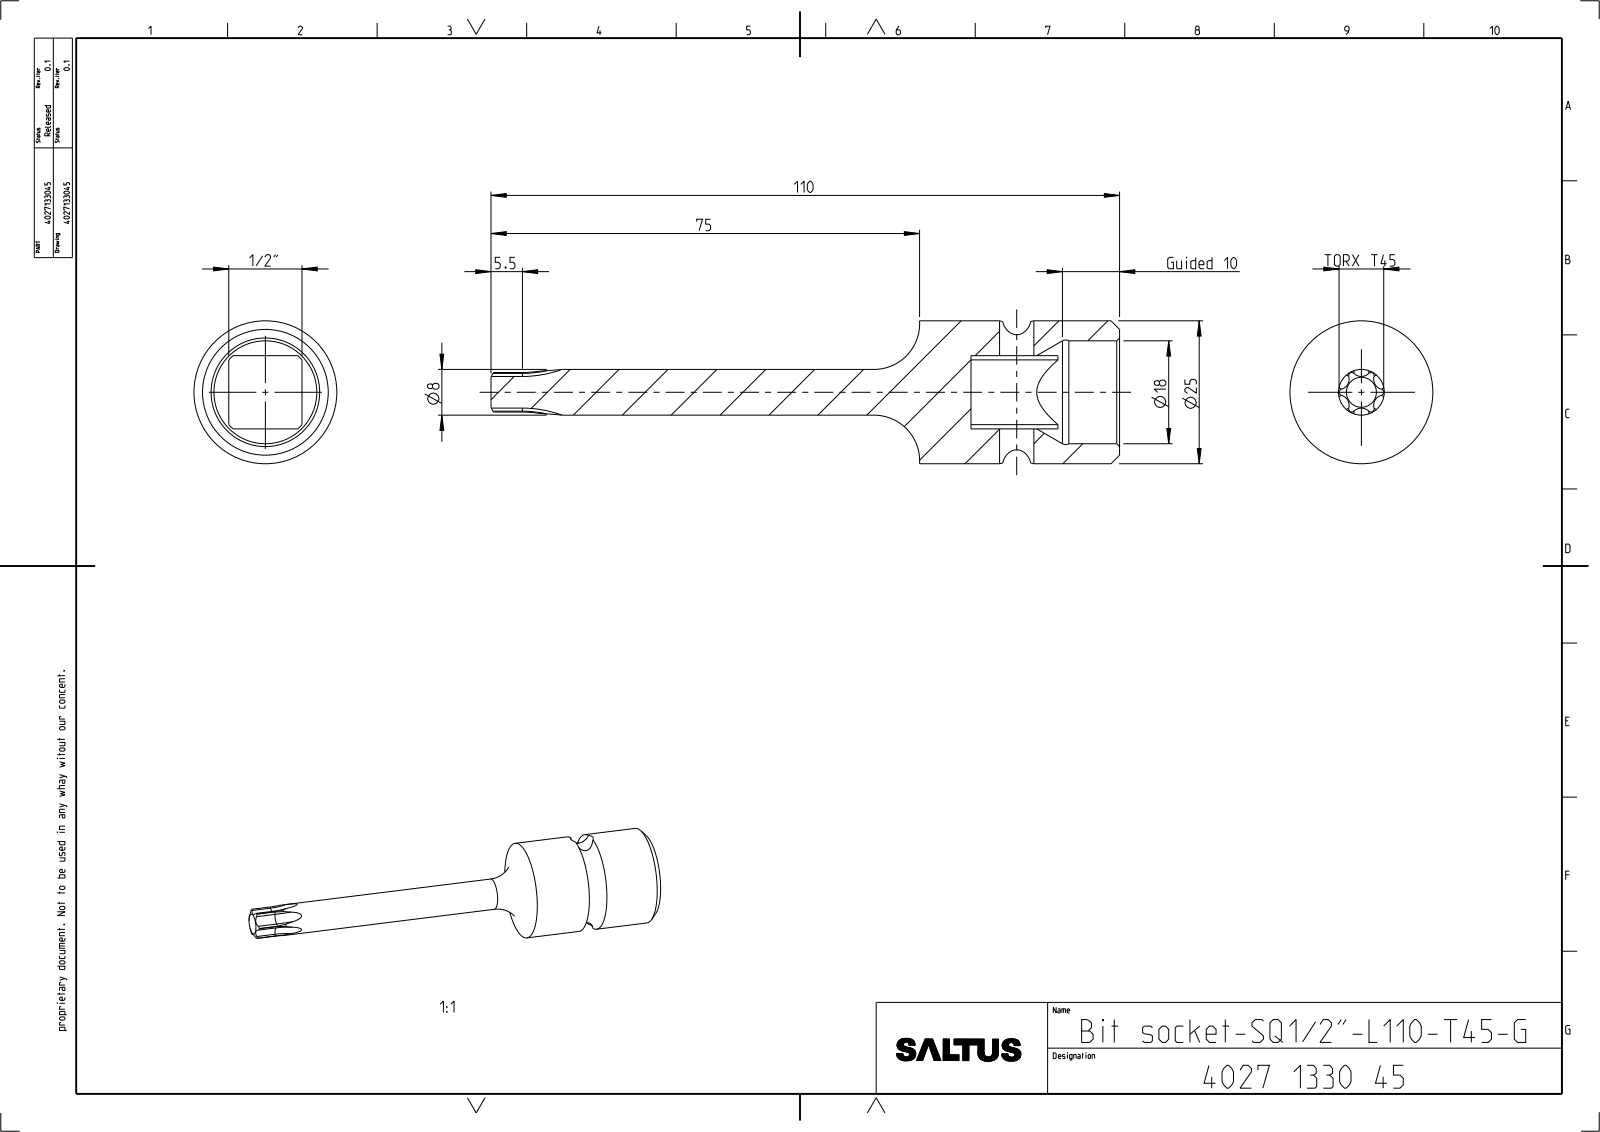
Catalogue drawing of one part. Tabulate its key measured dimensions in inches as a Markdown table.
| quantity | value |
| --- | --- |
| part name | 4027133045 |
| STEP written by | CREO PARAMETRIC BY PTC INC, 2022414 (CONFIG_CONTROL_DESIGN) |
| units | inches |
| bodies | 1 solid, 85 faces (7 planar, 40 cylindrical, 38 other) |
| overall size | 4.331 × 0.984 × 0.984 |
| volume | 0.92 in³ |
| surface area | 10.73 in² |
| round holes (diameter × count) | 0.236 × 1, 0.709 × 1 |
| round bosses / shafts (diameter × count) | 0.984 × 1, 0.315 × 1 |
| partial cylindrical surfaces (radius × count) | 0.021 × 12, 0.072 × 6, 0.154 × 1, 0.337 × 1 |
| main face-to-face distances | 0.505, 1.024, 4.331, 3.307 |
